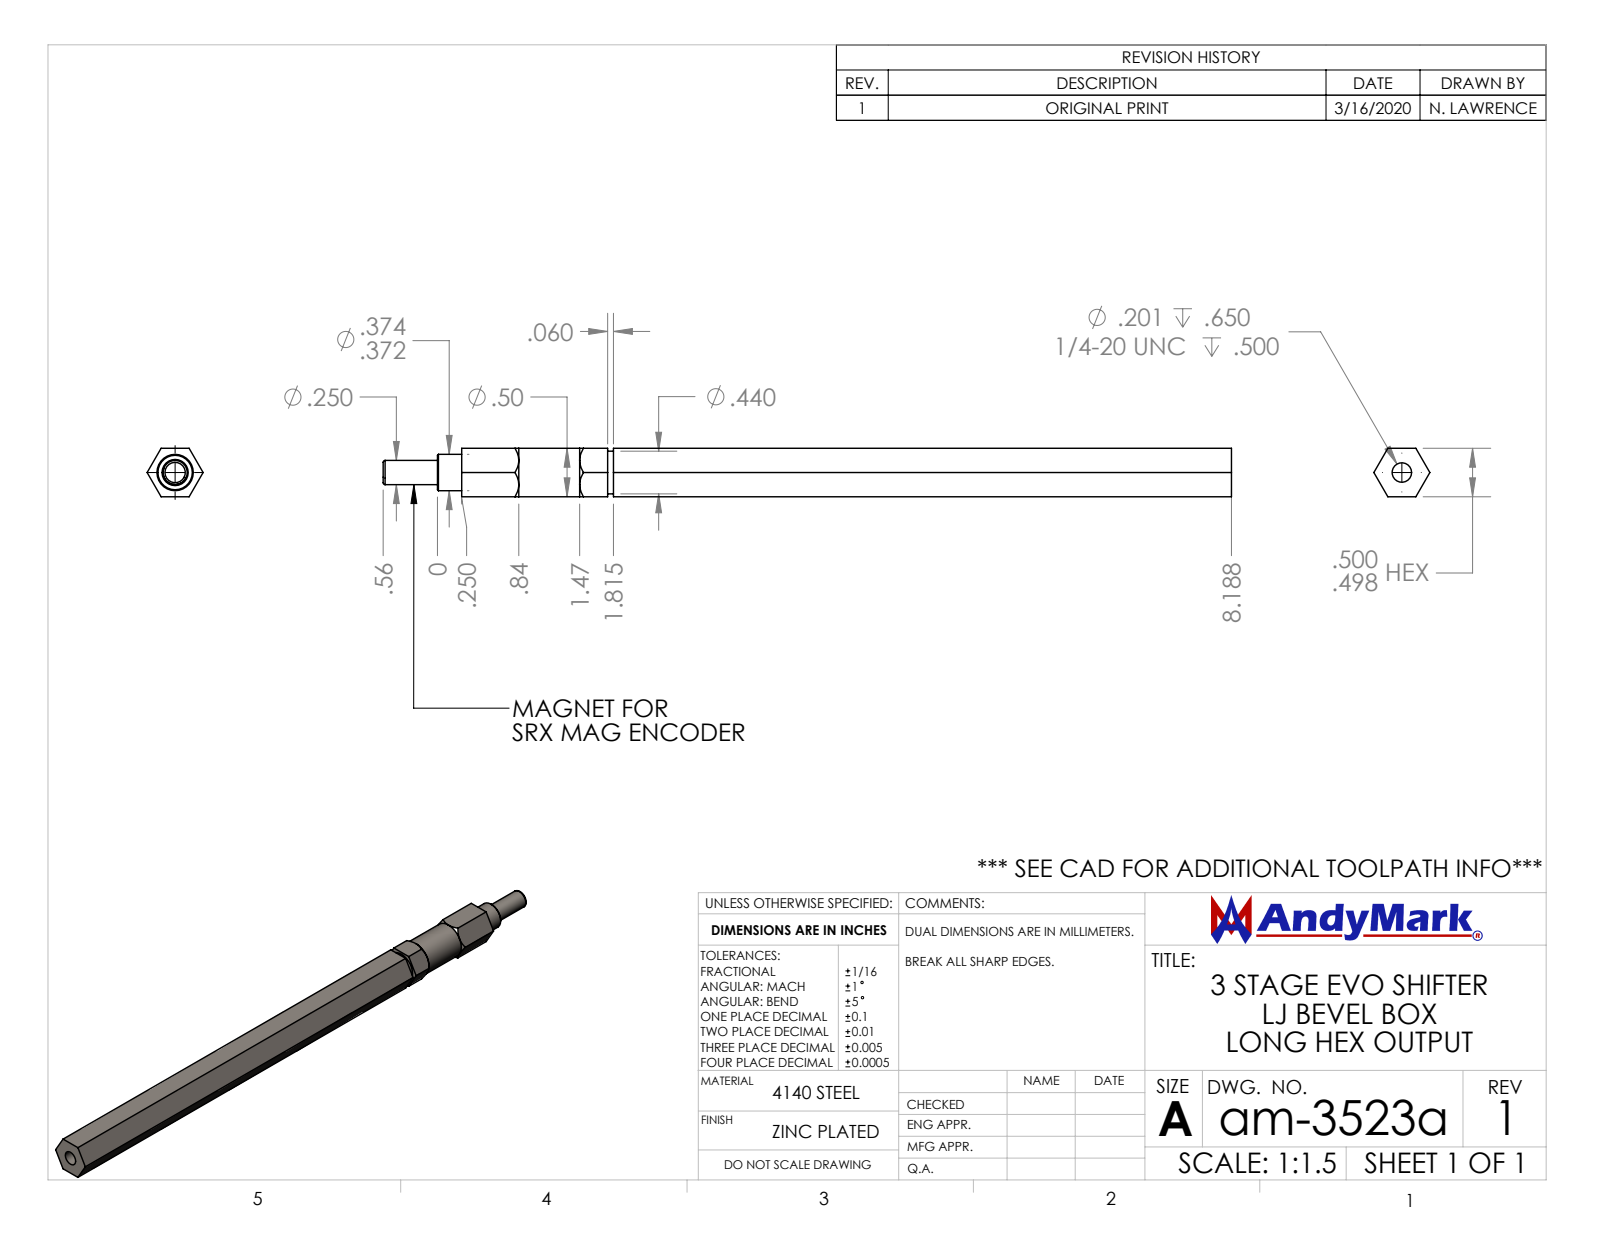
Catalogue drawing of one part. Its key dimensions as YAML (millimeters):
part_name: "am-3523a 3 Stage EVO Shifter and LJ Long Hex Output Shaft"
step_written_by: "SolidWorks 2019 (AUTOMOTIVE_DESIGN)"
units: millimeters
bodies: {solids: 2, faces: 49, planar: 26, cylindrical: 6, other: 17}
overall_size: [222.2, 14.66, 12.7]
volume: 28436
surface_area: 10396
round_holes:
  - {diameter: 5.11, count: 1}
  - {diameter: 6.35, count: 1}
round_bosses_or_shafts:
  - {diameter: 12.7, count: 1}
  - {diameter: 11.18, count: 1}
  - {diameter: 9.53, count: 1}
face_to_face_distances: [12.7, 201.63, 4.83, 196.8, 38.23, 33.4, 163.4, 39.75, 34.92, 1.52]
